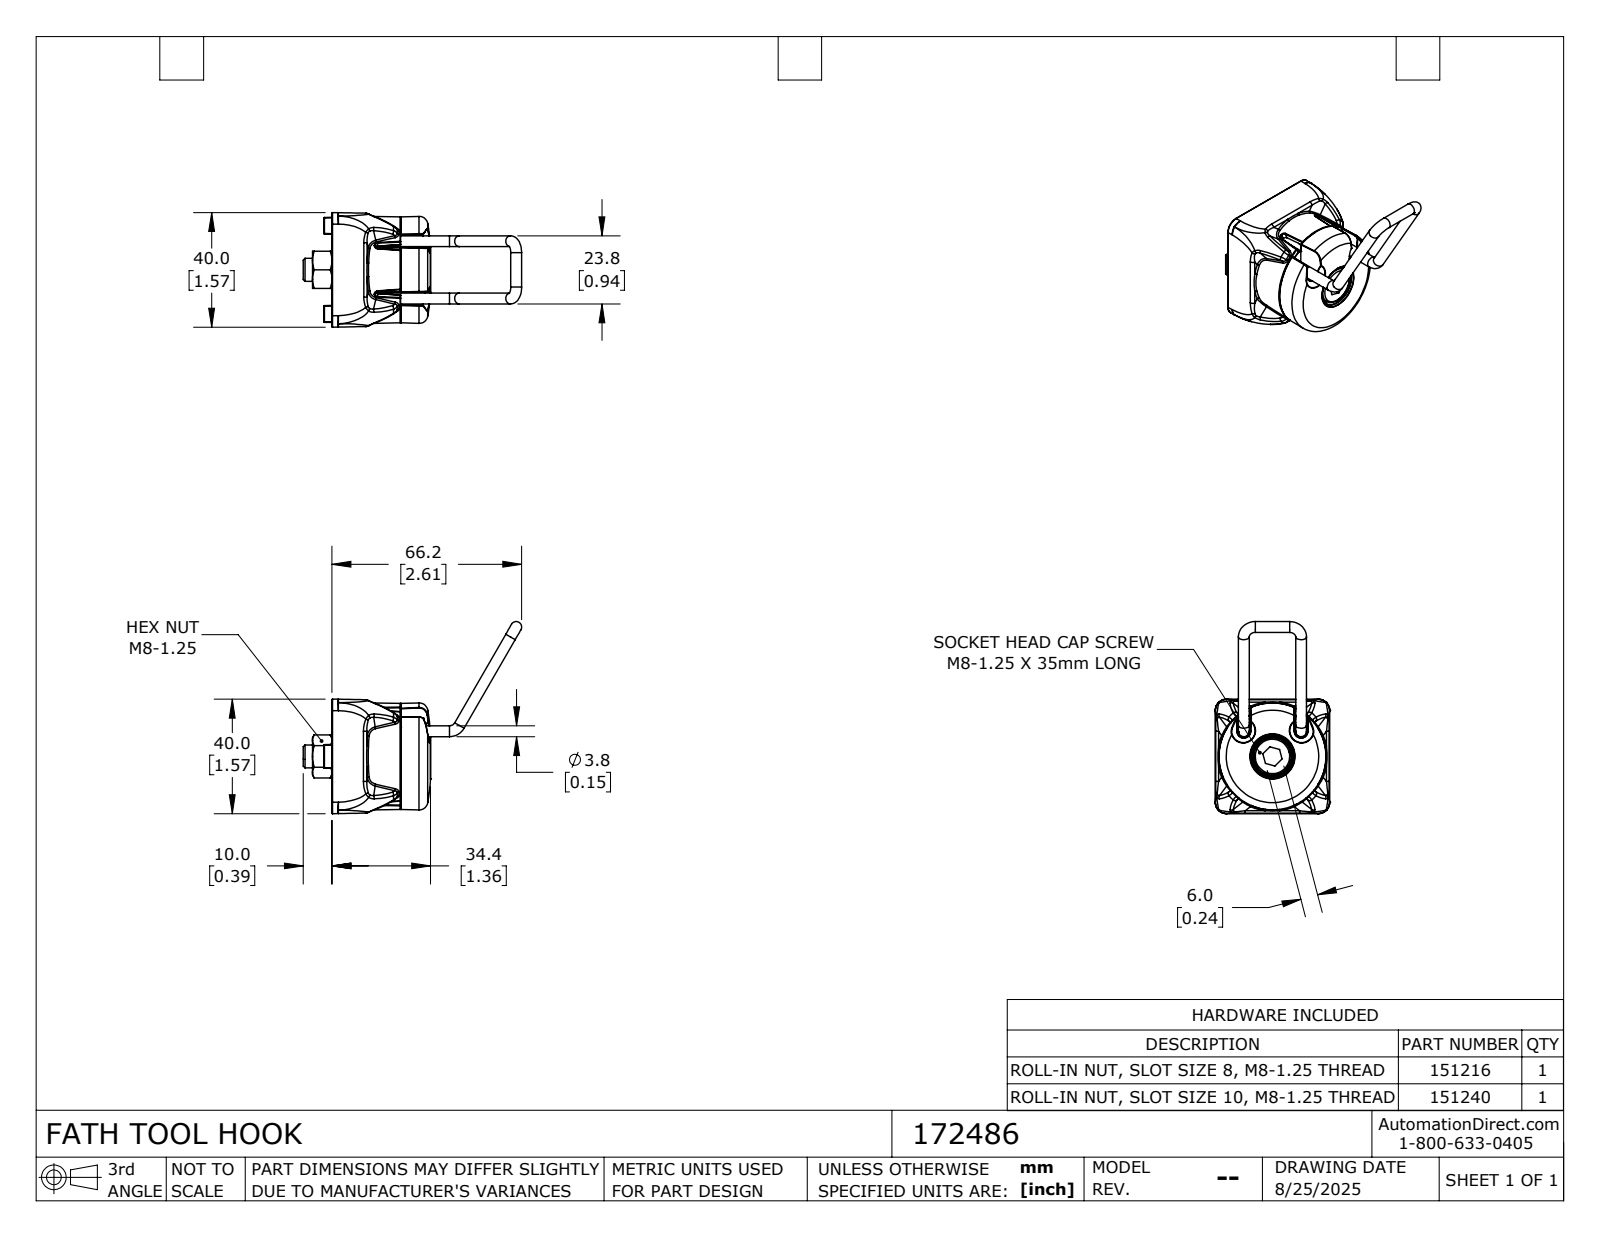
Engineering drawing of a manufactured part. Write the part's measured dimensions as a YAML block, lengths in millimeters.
part_name: "172486"
step_written_by: "SolidWorks 2024 (CONFIG_CONTROL_DESIGN)"
units: millimeters
bodies: {solids: 7, faces: 2382, planar: 359, cylindrical: 612, other: 1411}
overall_size: [76.25, 67.07, 40]
volume: 39521
surface_area: 22835
round_holes:
  - {diameter: 6.8, count: 1}
  - {diameter: 8, count: 1}
round_bosses_or_shafts:
  - {diameter: 3.8, count: 9}
  - {diameter: 13, count: 1}
partial_cylinders:
  - {radius: 0.2, count: 236}
  - {radius: 0.5, count: 200}
  - {radius: 1, count: 8}
  - {radius: 4, count: 8}
  - {radius: 1.2, count: 4}
  - {radius: 0.1, count: 2}
  - {radius: 2.15, count: 2}
face_to_face_distances: [30.8, 6, 17, 24, 8, 7, 18, 16, 6.9, 13.8]
